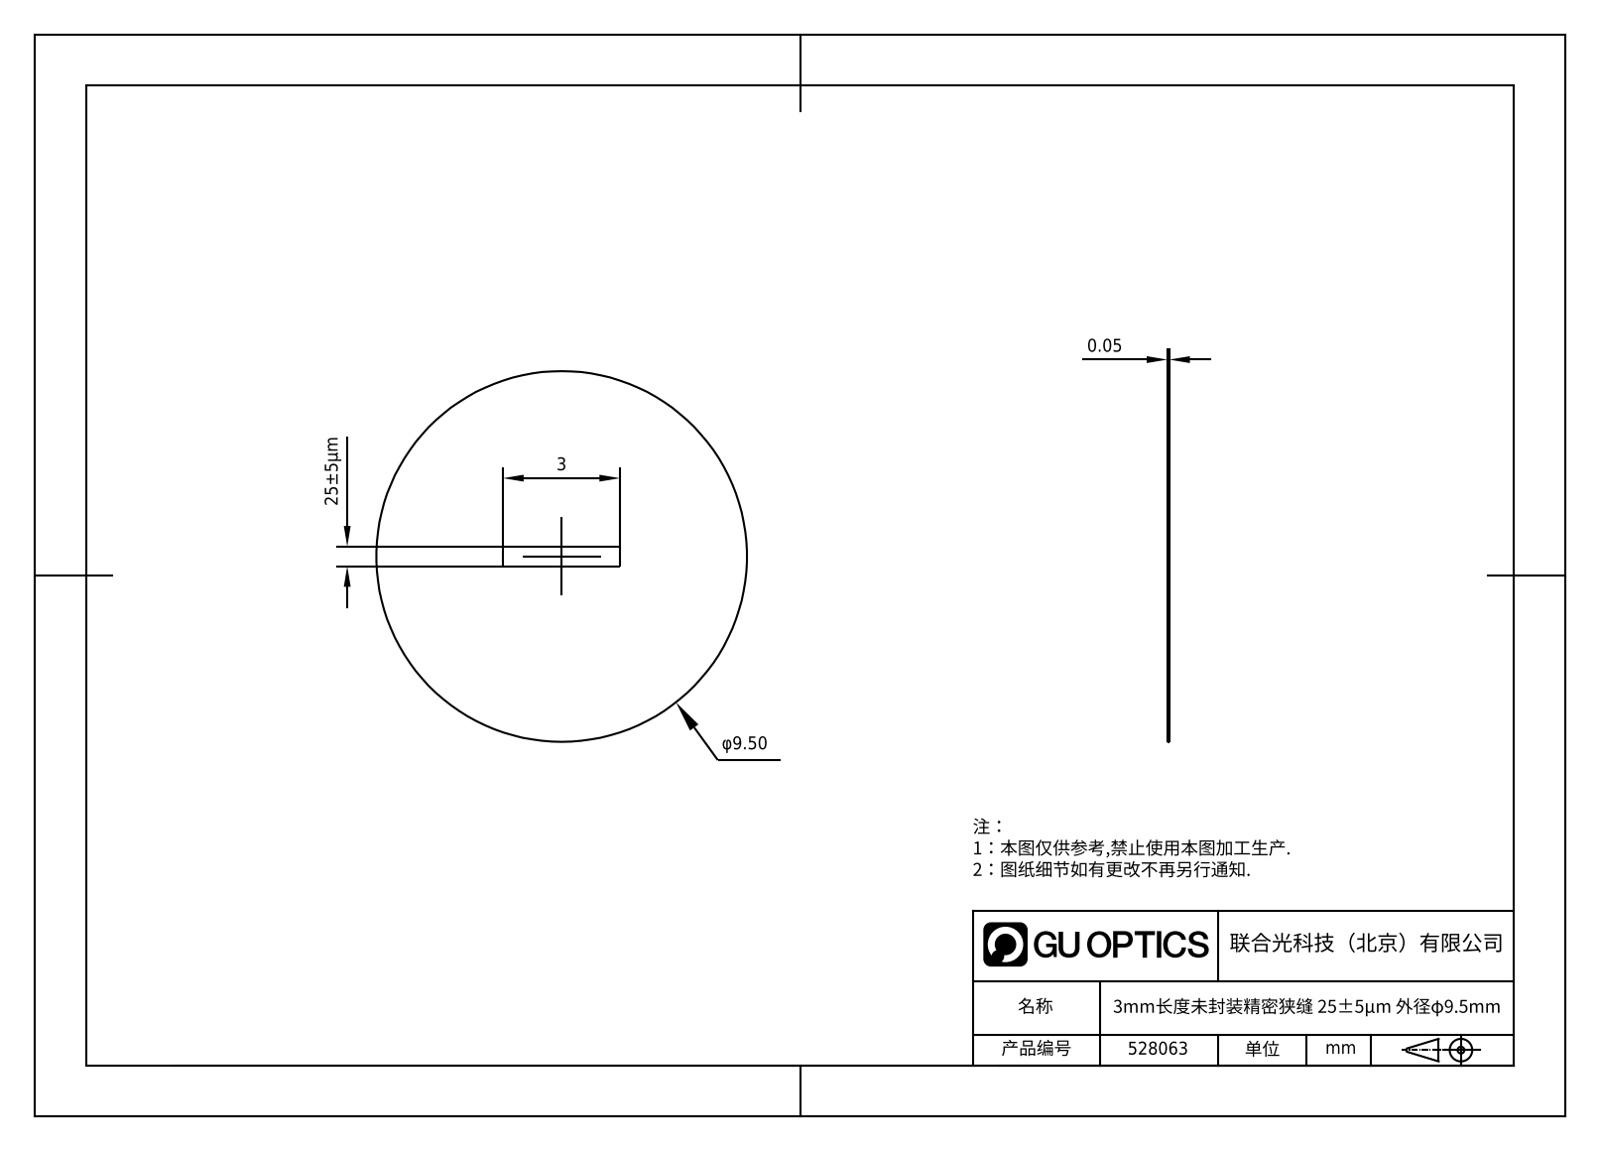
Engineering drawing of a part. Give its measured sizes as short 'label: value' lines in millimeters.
name: 1.5.4.4-ZXG-9.5-25
written by: SolidWorks 2021 (CONFIG_CONTROL_DESIGN)
unit: mm
bodies: 1 solid, 8 faces (6 planar, 2 cylindrical, 0 other)
size: 9.5 × 9.5 × 0.05
volume: 4 mm³; area: 143 mm²
bosses: 1× ⌀9.5
face distances: 3
